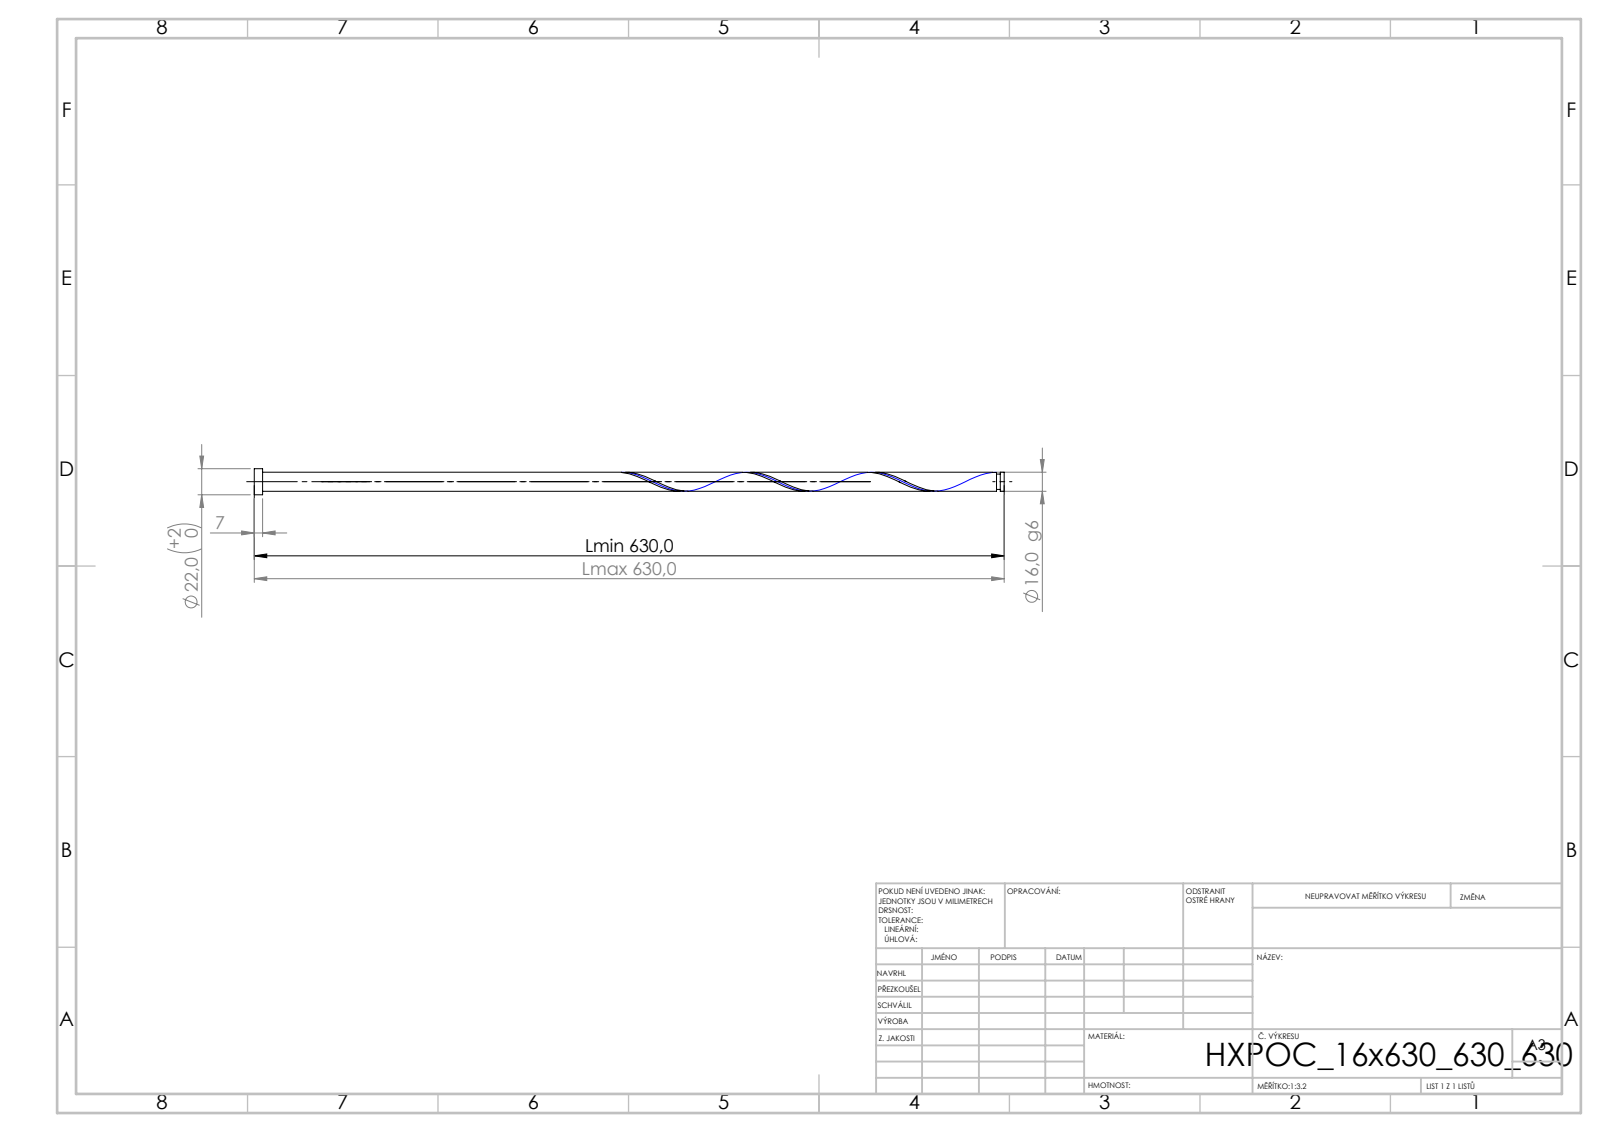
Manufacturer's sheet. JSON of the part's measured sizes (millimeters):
{"step_written_by": "SolidWorks 2019 (CONFIG_CONTROL_DESIGN)", "units": "millimeters", "bodies": {"solids": 1, "faces": 21, "planar": 6, "cylindrical": 14, "other": 1}, "overall_size": [630, 22, 22], "volume_mm3": 126478, "surface_area_mm2": 33221, "round_bosses_or_shafts": [[22, 1], [16, 1], [12.8, 1]], "face_to_face_distances": [630, 7, 623, 626.7, 619.7, 3.3, 623.5, 616.5, 3.2, 6.5]}
